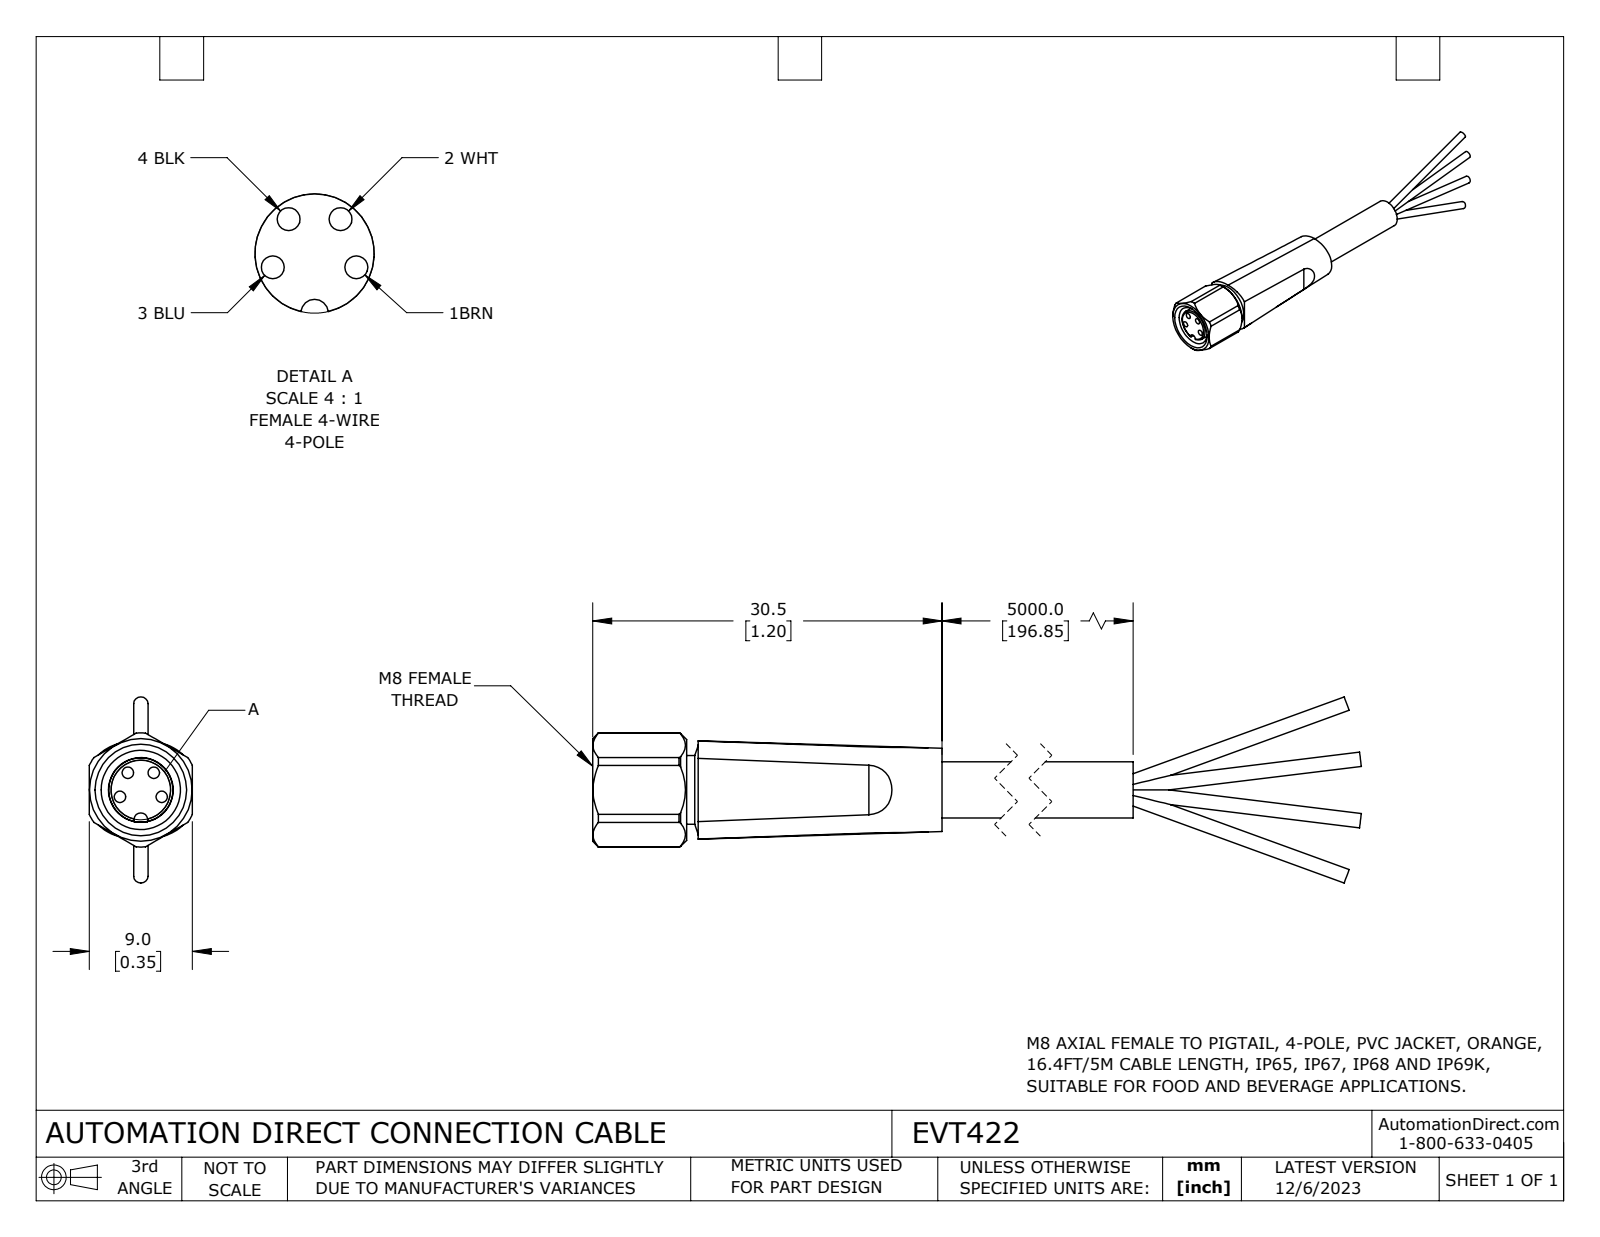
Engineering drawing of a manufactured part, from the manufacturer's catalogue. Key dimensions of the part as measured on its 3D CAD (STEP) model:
Part name (STEP PRODUCT): EVT422
STEP written by: SolidWorks 2023 (CONFIG_CONTROL_DESIGN)
Units: inches
Bodies: 1 solid, 82 faces (26 planar, 35 cylindrical, 21 other)
Overall size (bounding box): 2.694 × 0.64 × 0.354
Volume: 0.126 in³ · Surface area: 3.03 in²
Round holes (diameter × count): ⌀0.039 ×4, ⌀0.272 ×1
Round bosses / shafts (diameter × count): ⌀0.049 ×4, ⌀0.236 ×1, ⌀0.222 ×1, ⌀0.193 ×1
Partial cylindrical surfaces — rounded edges, fillets, slot ends (radius × count): R0.133 ×2, R0.024 ×1, R0.196 ×1
Main face-to-face distances: 0.354, 0.878, 0.303, 1.181, 1.89, 1.587, 0.709, 0.272, 0.031, 0.909
Hole centre spacings: 0.074, 0.076, 0.087, 0.143, 0.089, 0.143
